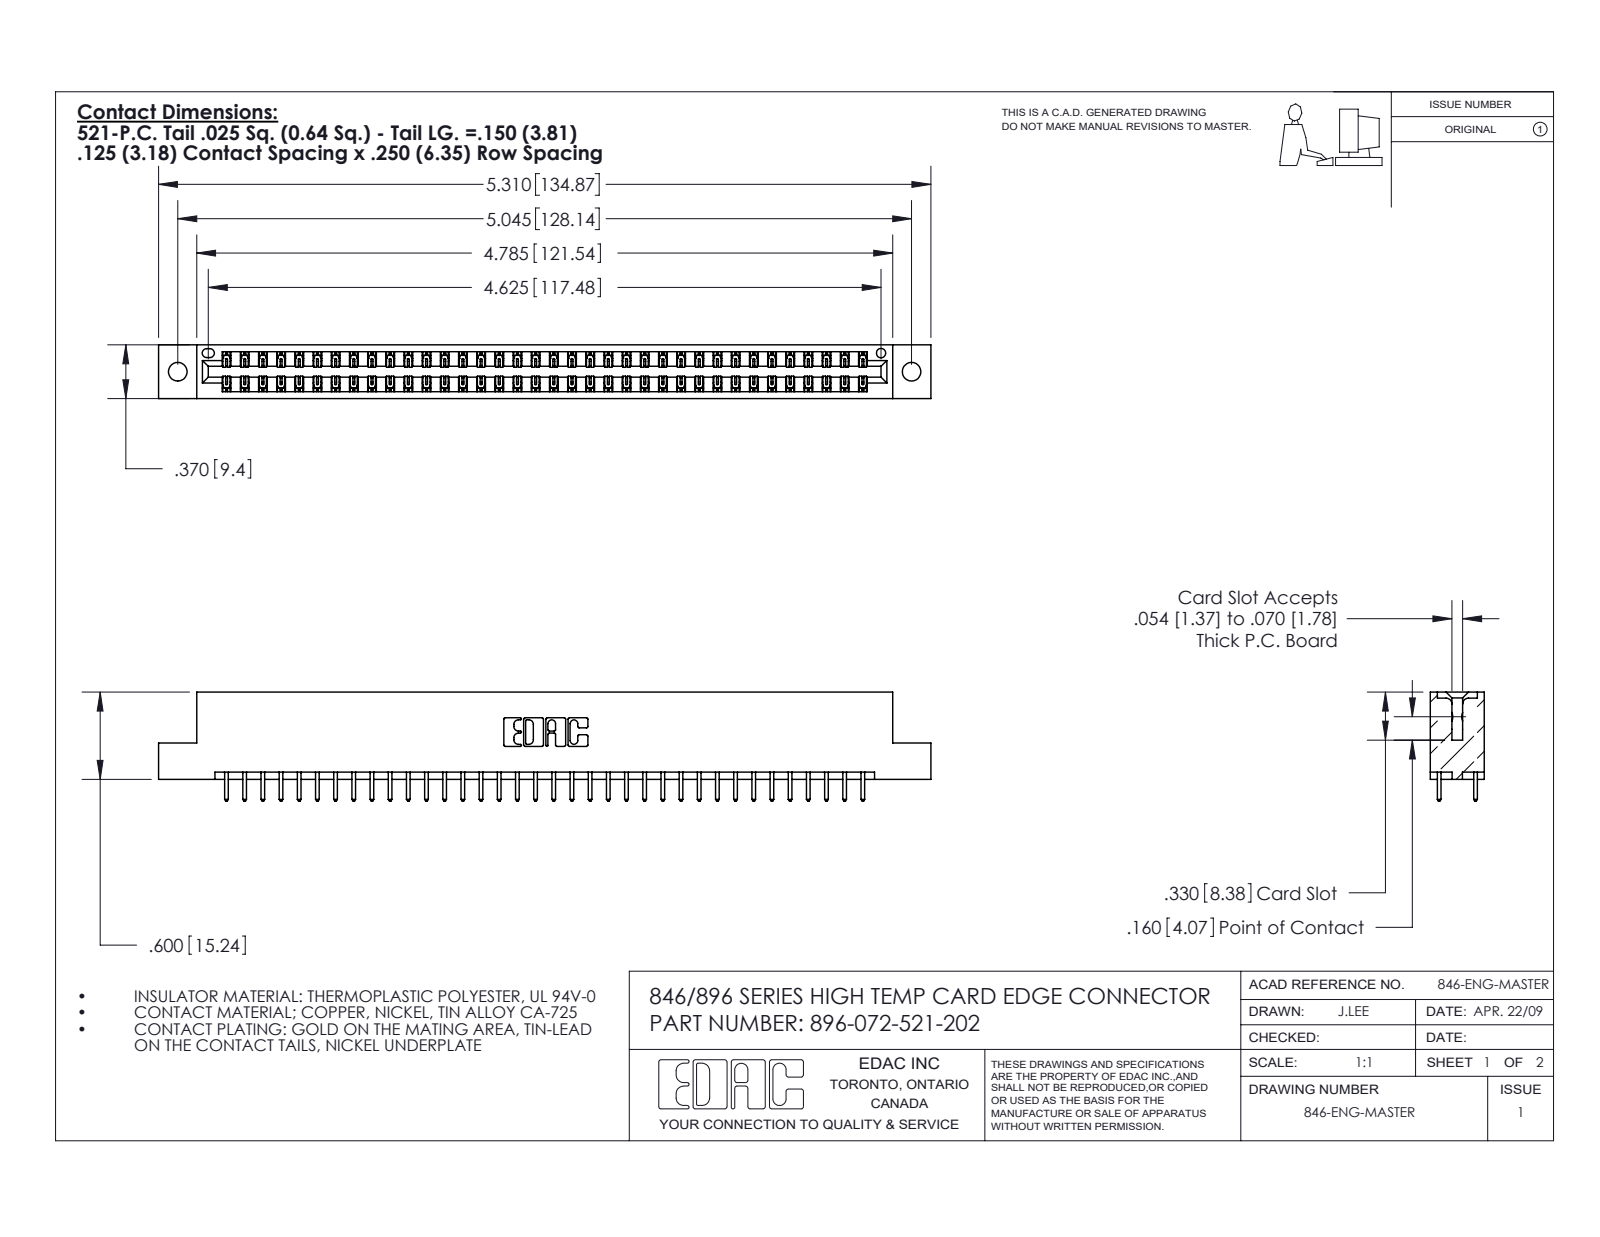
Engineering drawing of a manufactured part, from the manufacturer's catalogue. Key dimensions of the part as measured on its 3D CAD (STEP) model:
Part name (STEP PRODUCT): 346 Part_Flush Mounting Lugs - 0.128 Dia; 396-072-521-202; 345-292-001_345-293-121
STEP written by: SolidWorks 2016 (CONFIG_CONTROL_DESIGN)
Units: inches
Bodies: 73 solids, 3866 faces (2596 planar, 1270 cylindrical, 0 other)
Overall size (bounding box): 5.31 × 0.75 × 0.37
Volume: 0.796 in³ · Surface area: 26.91 in²
Round holes (diameter × count): ⌀0.128 ×2, ⌀0.064 ×1
Partial cylindrical surfaces — rounded edges, fillets, slot ends (radius × count): R0.006 ×108, R0.01 ×72, R0.01 ×22, R0.007 ×6, R0.031 ×6, R0.026 ×3, R0.014 ×2, R0.022 ×2
Main face-to-face distances: 0.048, 0.322, 0.25, 0.37, 0.072, 0.298, 0.025, 0.275, 0.148, 0.222
Hole centre spacings: 0.246, 4.836, 5.045
